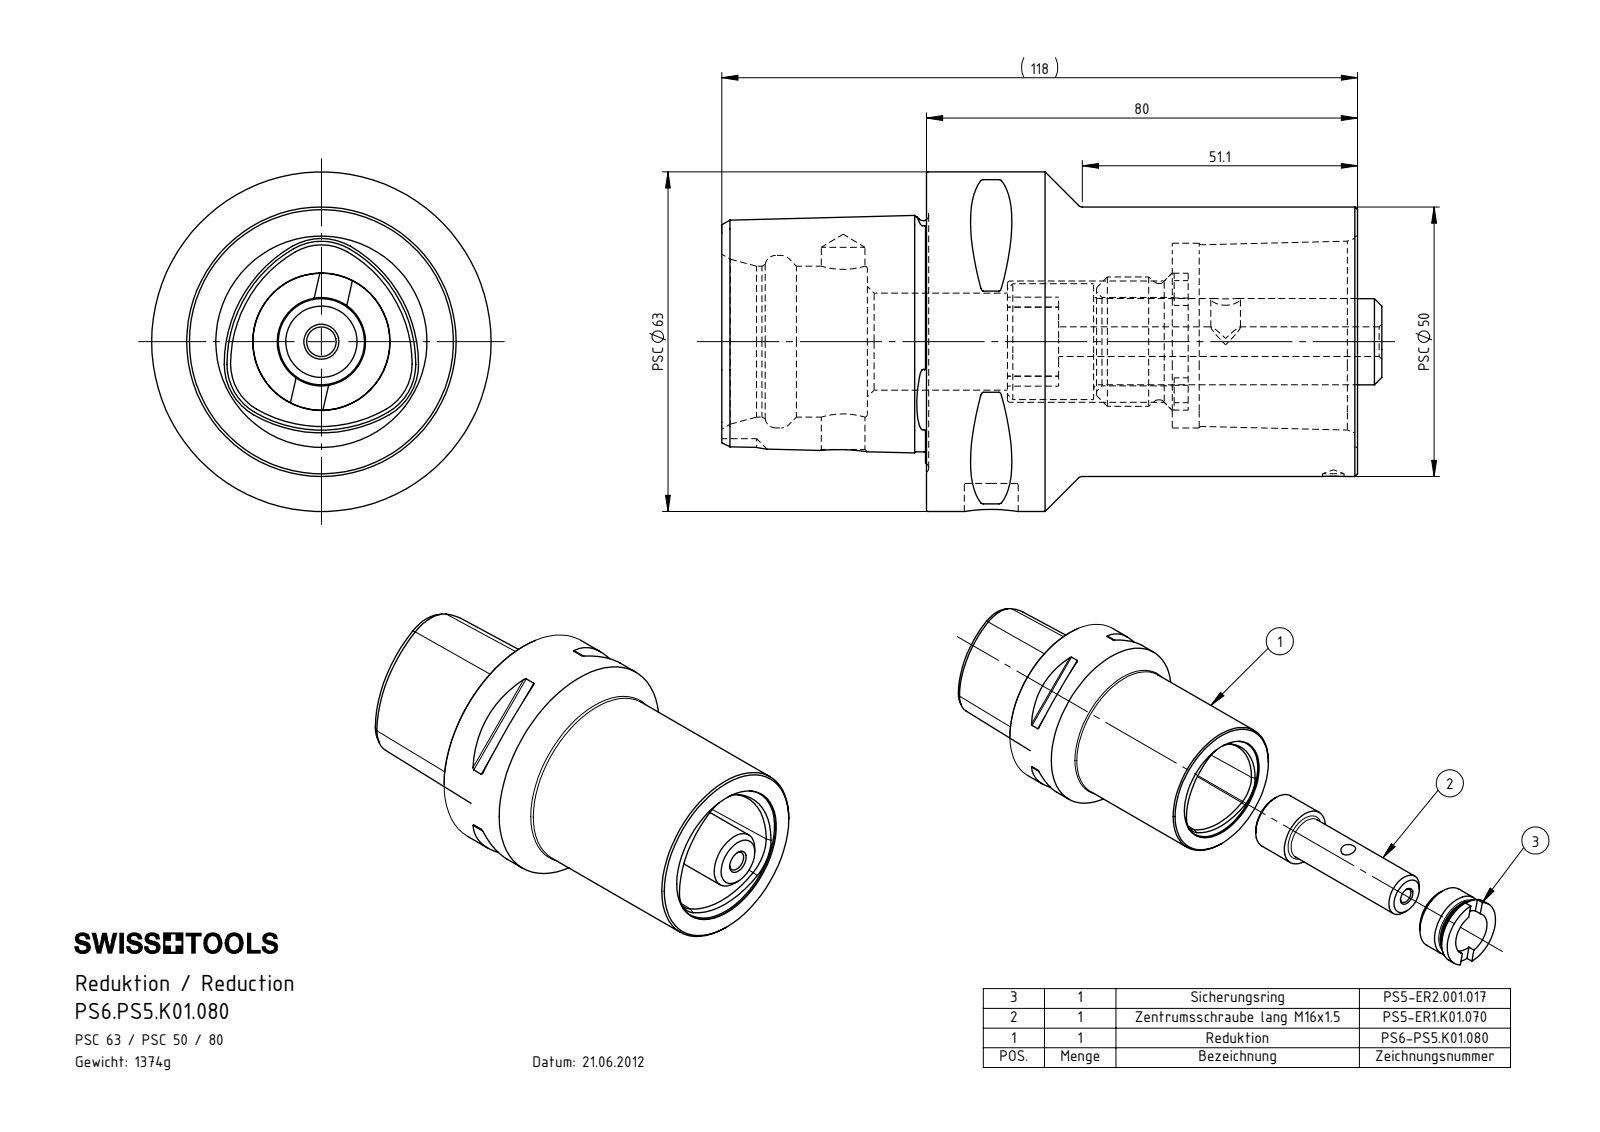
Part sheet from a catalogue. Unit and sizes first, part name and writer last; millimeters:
Units: millimetres
Overall size (bounding box): 122.5 × 63 × 63
Round holes (diameter × count): ⌀5.5 ×2, ⌀4 ×1, ⌀8.1 ×1, ⌀10 ×1, ⌀16.4 ×1, ⌀18 ×1, ⌀22.5 ×1, ⌀28 ×1, ⌀32 ×1, ⌀39.2 ×1
Round bosses / shafts (diameter × count): ⌀63 ×1, ⌀50 ×1, ⌀25.4 ×1, ⌀24 ×1, ⌀21.6 ×1, ⌀21.5 ×1, ⌀16 ×1
Partial cylindrical surfaces — rounded edges, fillets, slot ends (radius × count): R0.5 ×8, R6 ×7, R2.3 ×6, R9.9 ×3, R24.38 ×3
Main face-to-face distances: 80, 38, 118, 83.6, 45.6, 34.4, 24.88, 33.55, 27, 11
Hole centre spacings: 27.5, 63.5, 91
Volume: 186 541 mm³ · Surface area: 42 367 mm²
Bodies: 3 solids, 236 faces (36 planar, 71 cylindrical, 129 other)
Part name (STEP PRODUCT): PS5-ER1.K01.070_A_PreviewCfg; PS5-ER2.001.017_A; PS6-PS5.K01.080_B; PS6.PS5.K01.080
STEP written by: SolidWorks 2022 (AUTOMOTIVE_DESIGN)
